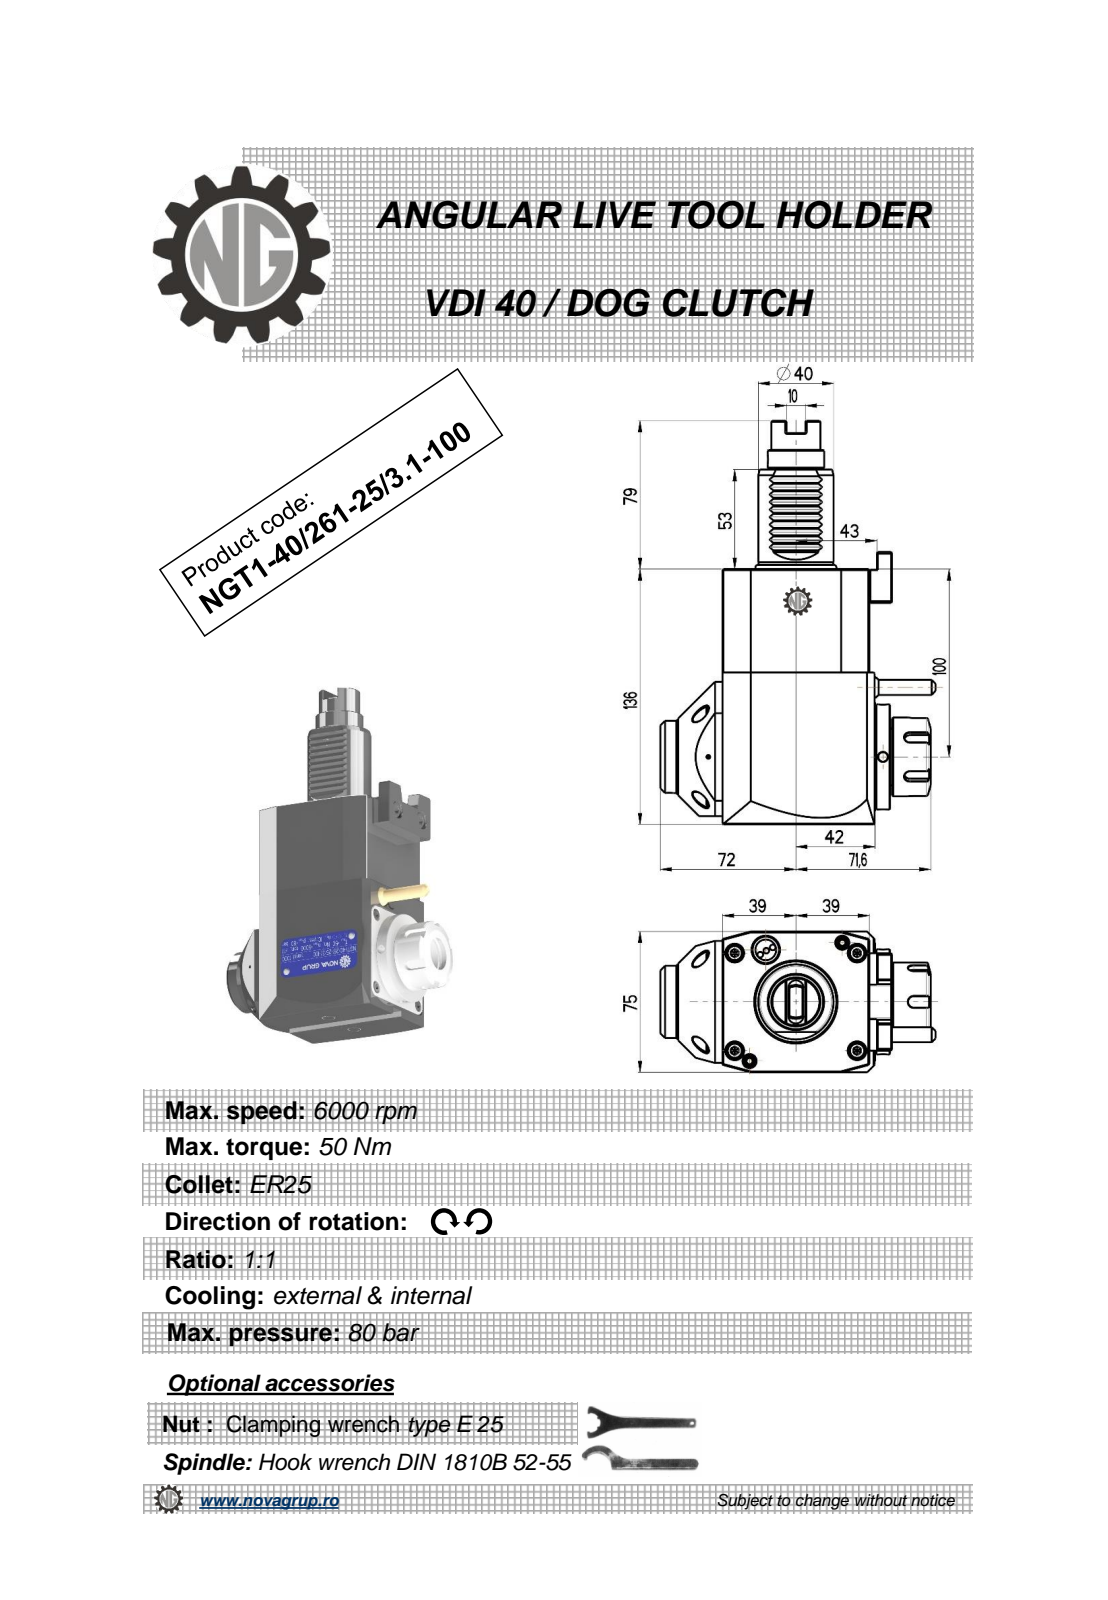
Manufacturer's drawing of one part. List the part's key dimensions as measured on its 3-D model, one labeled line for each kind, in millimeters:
Part name (STEP PRODUCT): NGT1_40_261_25_3_1_100
STEP written by: PRO/ENGINEER BY PARAMETRIC TECHNOLOGY CORPORATION, 2010280 (CONFIG_CONTROL_DESIGN)
Units: millimetres
Bodies: 1 solid, 404 faces (199 planar, 76 cylindrical, 129 other)
Overall size (bounding box): 215 × 146.14 × 75
Volume: 1 015 000 mm³ · Surface area: 77 978 mm²
Round holes (diameter × count): ⌀5 ×3, ⌀3 ×1, ⌀4.2 ×1, ⌀20.3 ×1
Round bosses / shafts (diameter × count): ⌀56 ×1, ⌀43 ×1, ⌀42 ×1, ⌀40 ×1, ⌀38.5 ×1, ⌀33 ×1, ⌀30 ×1, ⌀26 ×1
Partial cylindrical surfaces — rounded edges, fillets, slot ends (radius × count): R0.3 ×10, R0.22 ×6, R0.26 ×6, R3 ×5, R0.5 ×3, R1 ×2, R12.5 ×1, R40 ×1
Main face-to-face distances: 75, 136, 78, 81, 3, 0.5, 8, 11, 84.88, 8.2
Hole centre spacings: 40.93, 122.75, 158.5
